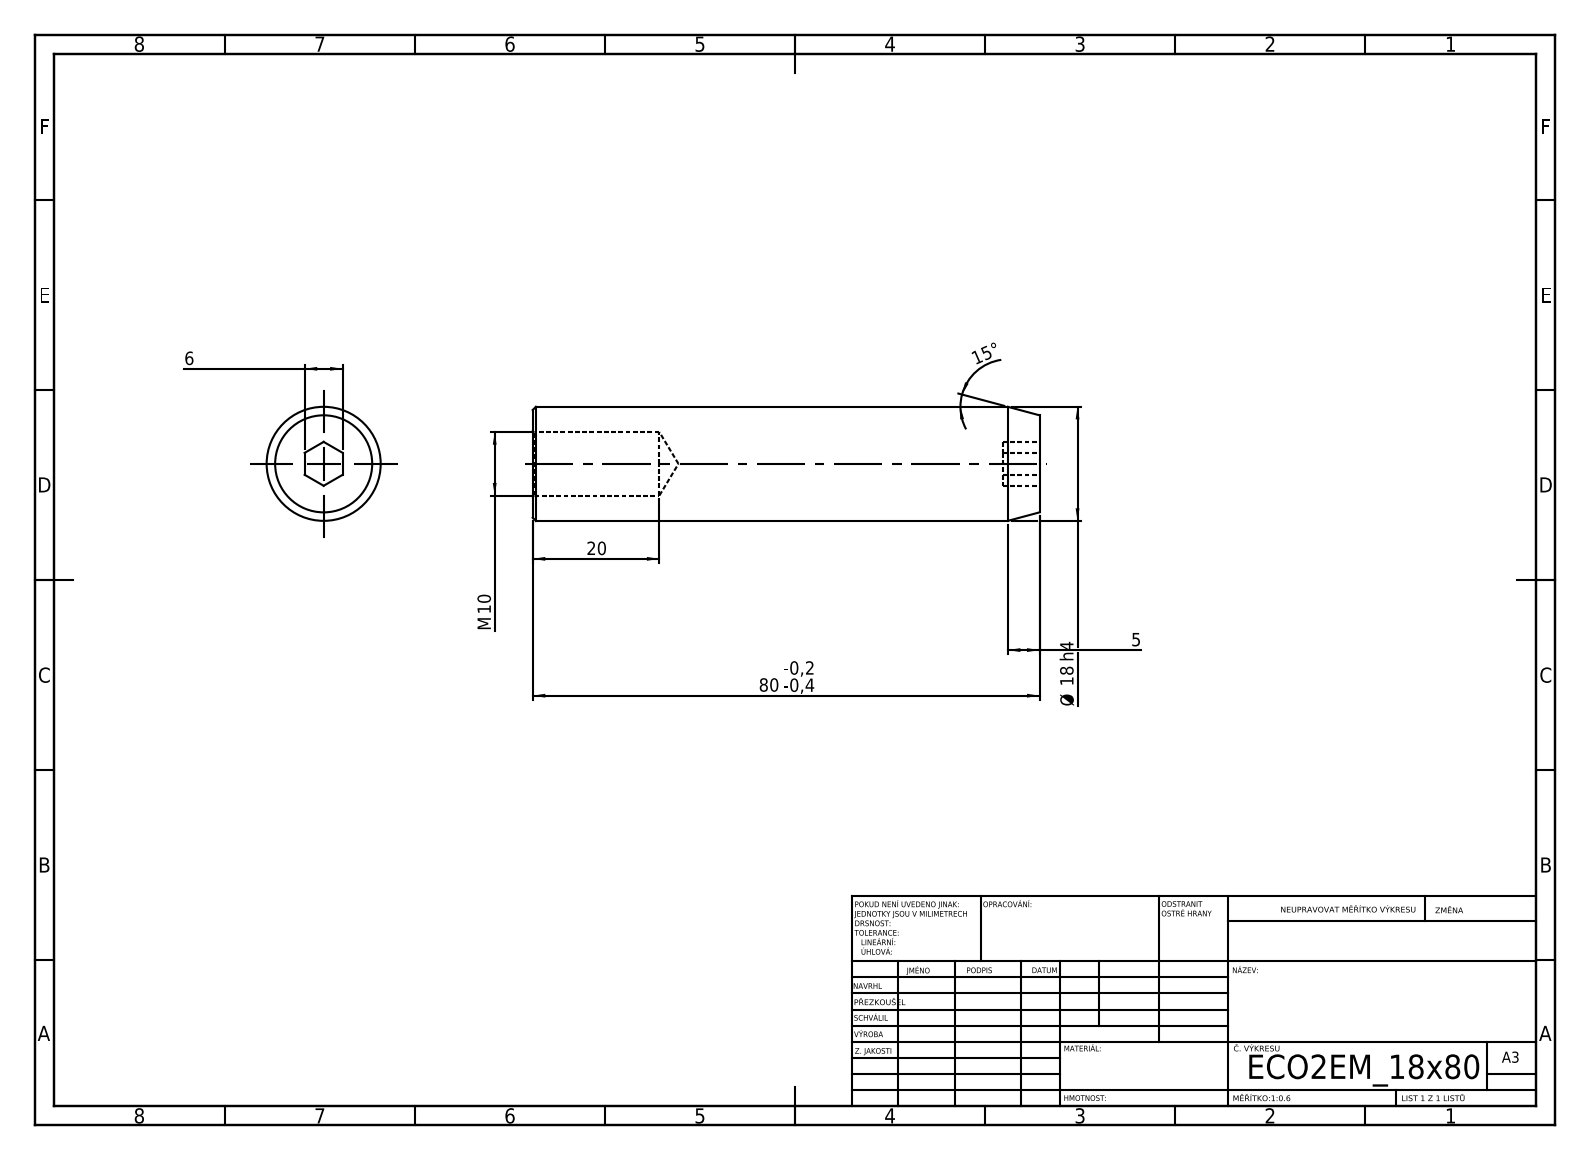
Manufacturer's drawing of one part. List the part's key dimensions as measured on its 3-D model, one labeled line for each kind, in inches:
STEP written by: SolidWorks 2019 (CONFIG_CONTROL_DESIGN)
Units: inches
Bodies: 1 solid, 21 faces (9 planar, 4 cylindrical, 8 other)
Overall size (bounding box): 3.15 × 0.709 × 0.709
Volume: 1.119 in³ · Surface area: 8.823 in²
Round holes (diameter × count): ⌀0.394 ×1
Round bosses / shafts (diameter × count): ⌀0.709 ×1
Main face-to-face distances: 3.15, 0.236, 0.228, 2.921
